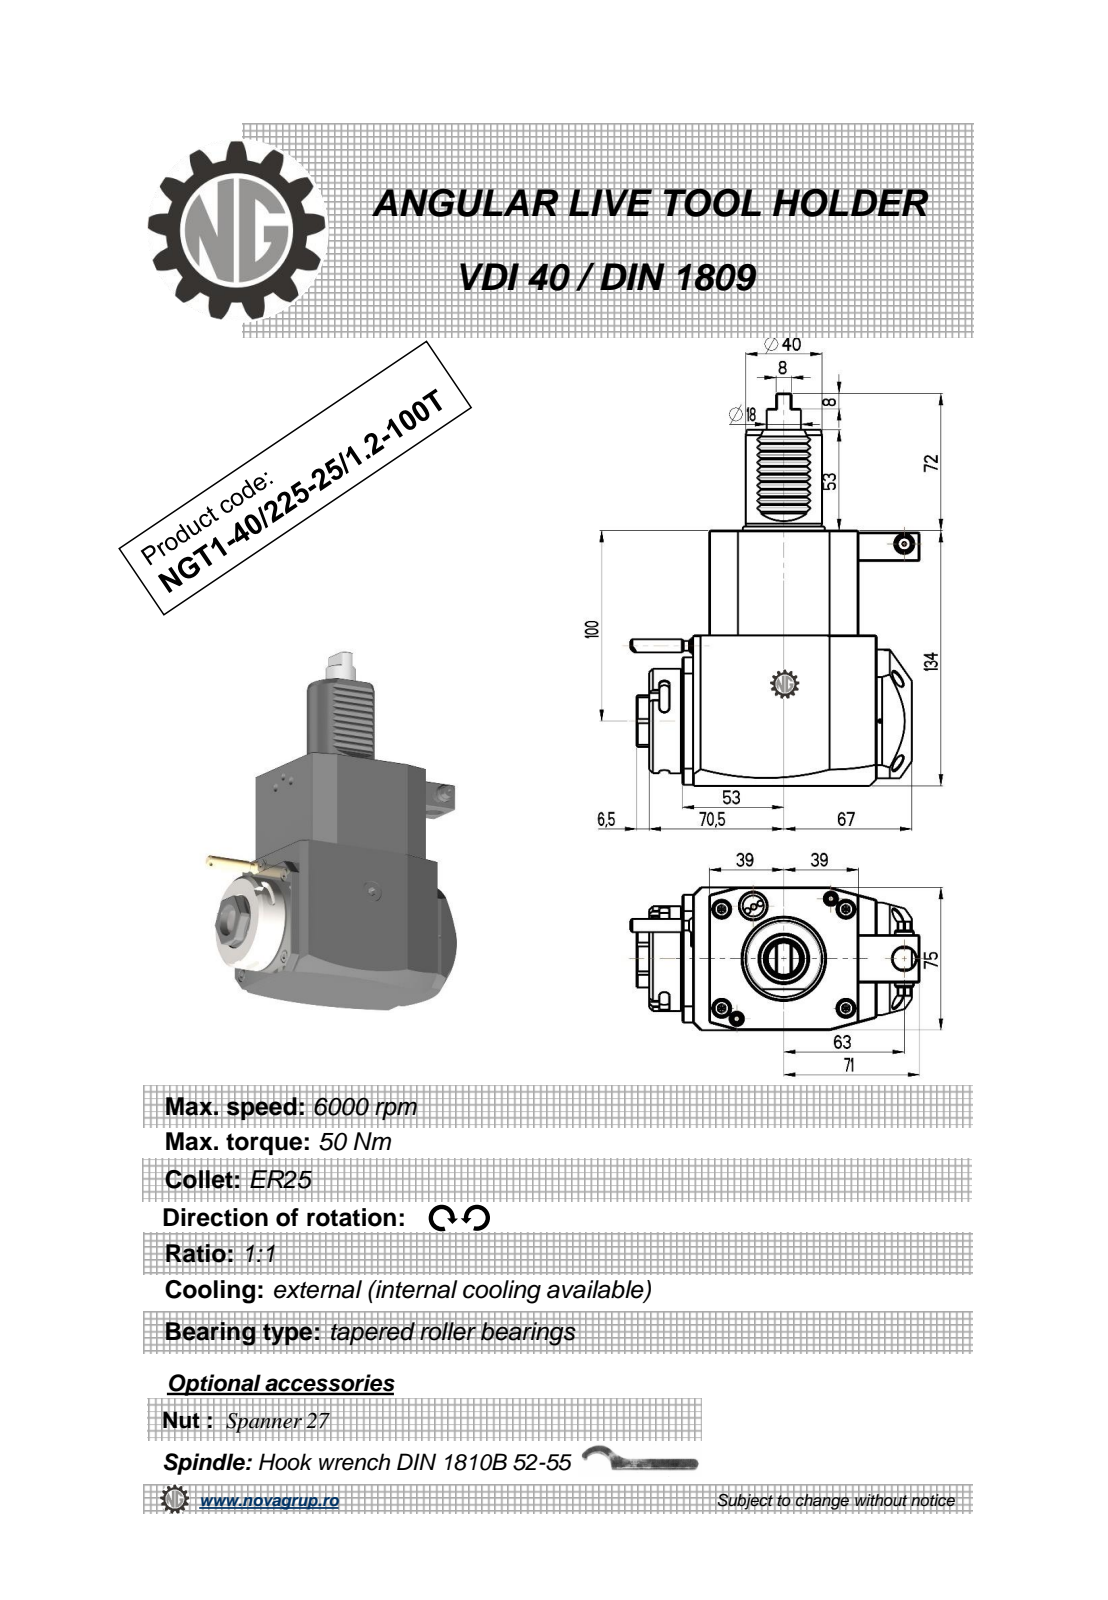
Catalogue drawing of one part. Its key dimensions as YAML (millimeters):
part_name: "NGT1_40_225_25_1_2_100T"
step_written_by: "PRO/ENGINEER BY PARAMETRIC TECHNOLOGY CORPORATION, 2010280 (CONFIG_CONTROL_DESIGN)"
units: millimeters
bodies: {solids: 1, faces: 347, planar: 183, cylindrical: 90, other: 74}
overall_size: [206, 151.33, 75]
volume: 1064000
surface_area: 76427
round_holes:
  - {diameter: 2, count: 1}
  - {diameter: 2.5, count: 1}
  - {diameter: 3, count: 1}
  - {diameter: 4.5, count: 1}
  - {diameter: 9.5, count: 1}
  - {diameter: 12, count: 1}
  - {diameter: 18, count: 1}
round_bosses_or_shafts:
  - {diameter: 8, count: 2}
  - {diameter: 55, count: 1}
  - {diameter: 48, count: 1}
  - {diameter: 40, count: 1}
  - {diameter: 17.8, count: 1}
  - {diameter: 10, count: 1}
  - {diameter: 7, count: 1}
  - {diameter: 5, count: 1}
partial_cylinders:
  - {radius: 0.3, count: 10}
  - {radius: 2.5, count: 6}
  - {radius: 0.8, count: 2}
  - {radius: 180, count: 2}
  - {radius: 0.5, count: 1}
  - {radius: 3.85, count: 1}
  - {radius: 4.25, count: 1}
  - {radius: 15, count: 1}
face_to_face_distances: [75, 134, 78, 14, 92, 17.5, 31.5, 84.88, 109.5, 4]
hole_center_spacings: [43.2, 55.81, 92.5]
